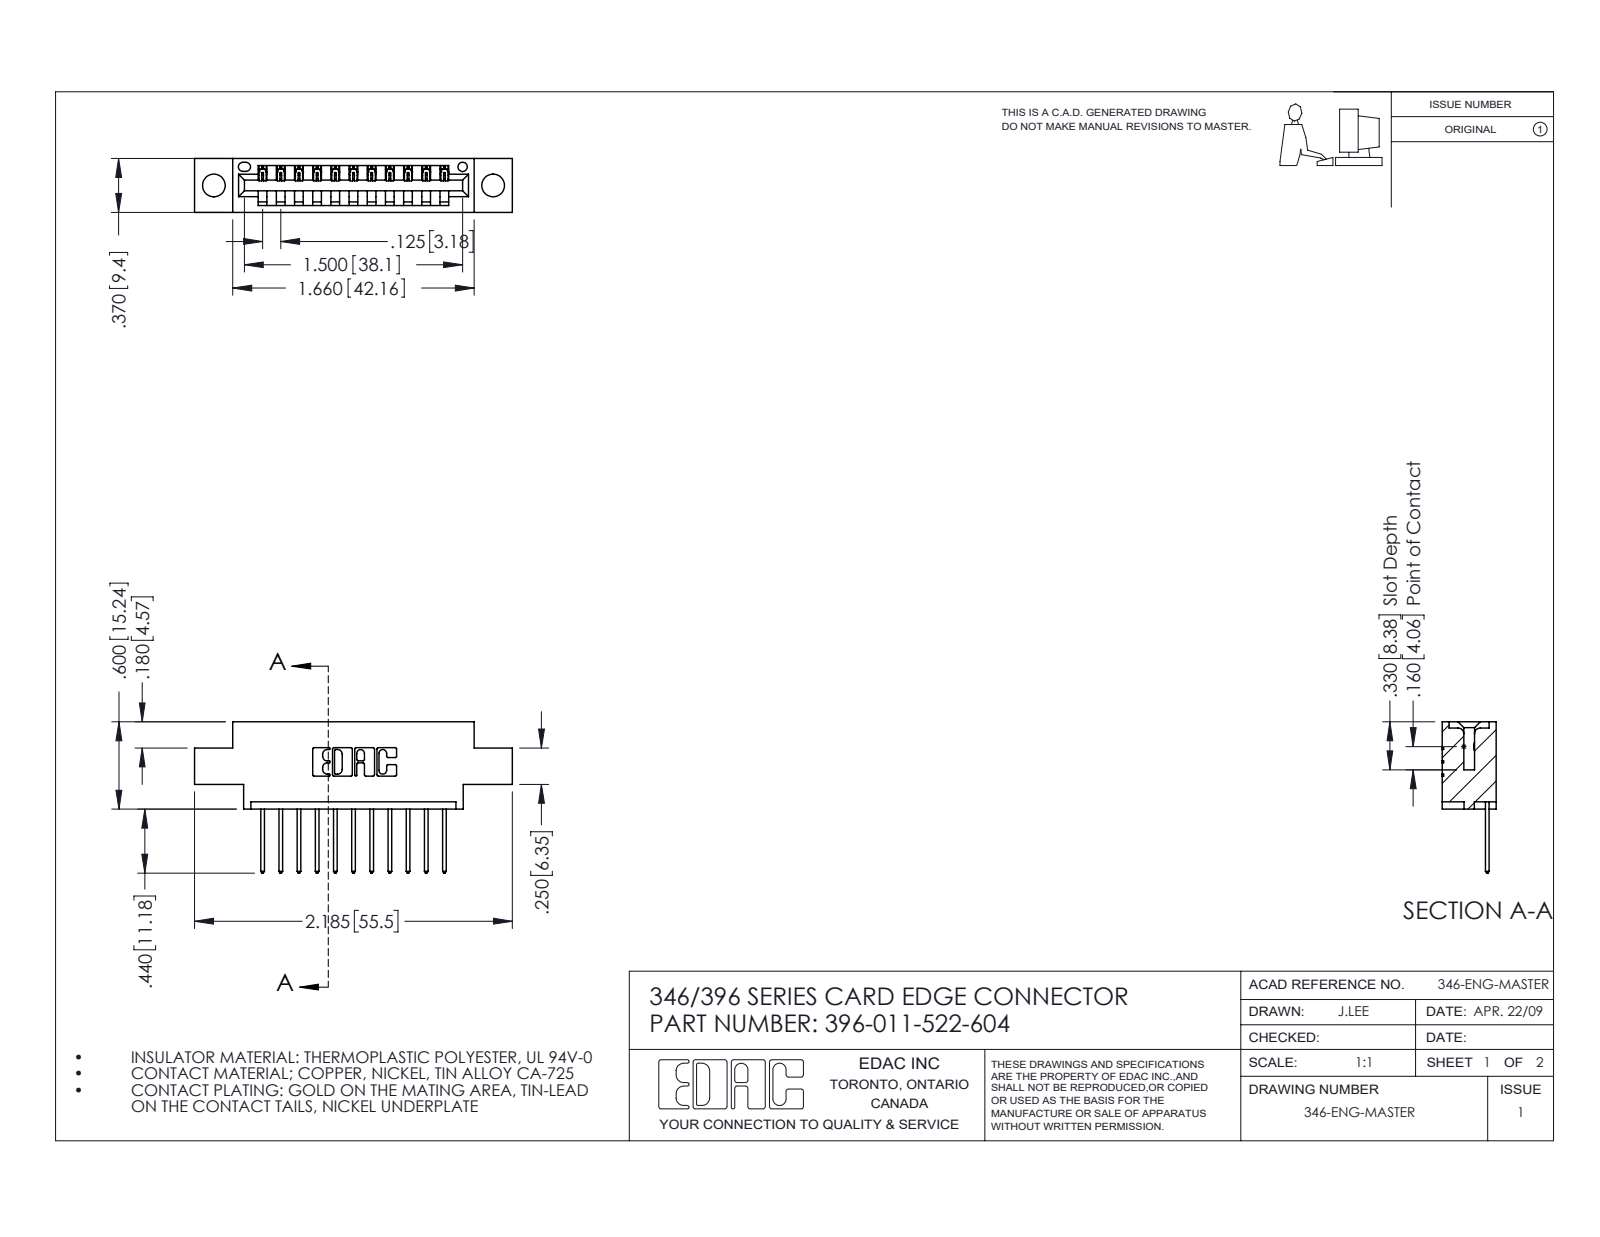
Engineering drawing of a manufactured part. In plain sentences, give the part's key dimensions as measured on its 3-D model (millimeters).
The part is named "346 Part_0.170 Offset - 0.156 Dia-TH; 345-292-001_345-293-122; 396-011-522-604". Its 3-D file was written by "SolidWorks 2016 (CONFIG_CONTROL_DESIGN)". It is 12 solids with 764 faces: 520 planar, 244 cylindrical and 0 other. Overall it measures 55.5 by 26.4 by 9.4 millimeters. Its volume is 4 850 cubic millimeters and its surface area 5 743 square millimeters. Round holes: 2 of diameter 4, 1 of diameter 1.6. Partial cylindrical surfaces (rounded edges, fillets, slot ends): 22 of radius 0.2, 22 of radius 0.3, 22 of radius 0.3, 6 of radius 0.2, 6 of radius 0.8, 3 of radius 0.7, 2 of radius 0.8, 2 of radius 1. The main face-to-face distances are 6.4, 9.4, 1.2, 8.2, 1.8, 7.6, 0.6, 3.8, 5.6, 2.5. The hole center spacings are 6.2, 43.6, 48.8.
